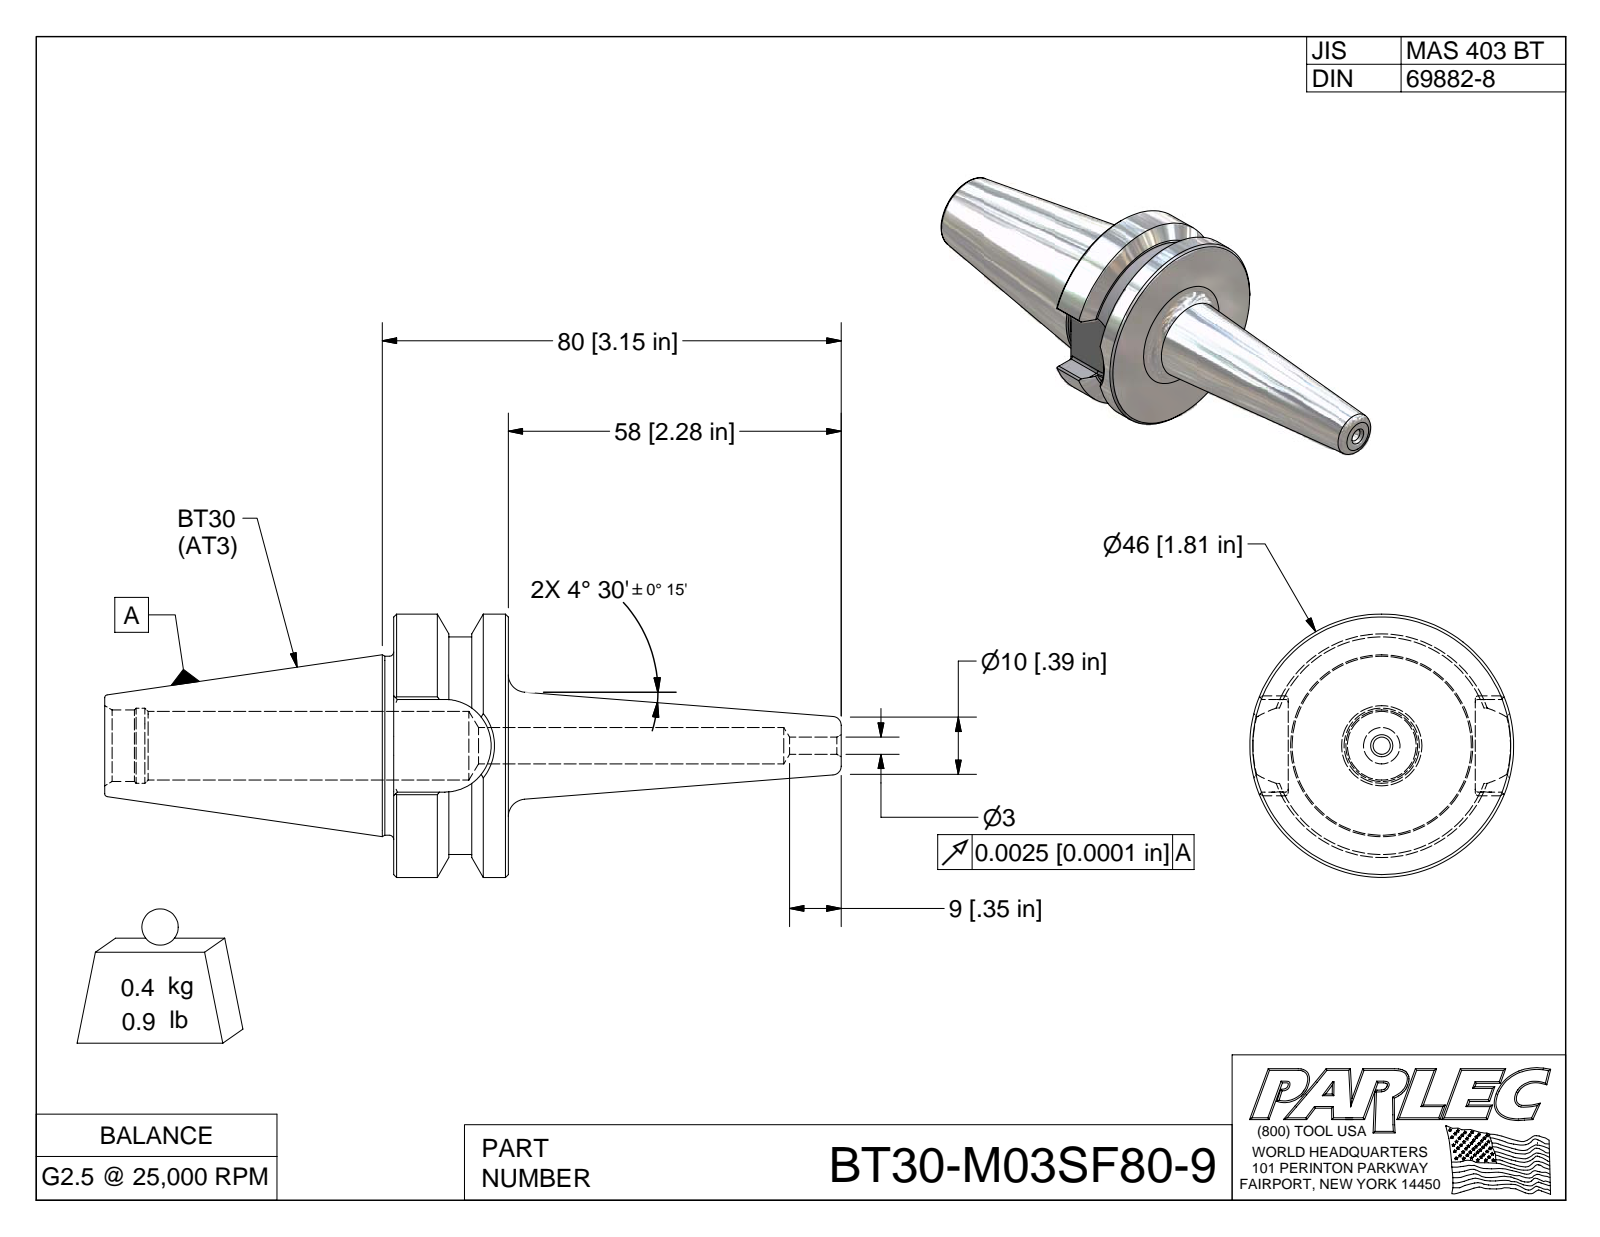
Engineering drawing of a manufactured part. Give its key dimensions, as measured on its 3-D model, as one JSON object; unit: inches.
{"part_name": "BT30-M03SF80-9; BT30-M03SF80-9-1", "step_written_by": "Autodesk Inventor 2009 (AUTOMOTIVE_DESIGN)", "units": "inches", "bodies": {"solids": 1, "faces": 68, "planar": 23, "cylindrical": 18, "other": 27}, "overall_size": [5.056, 1.811, 1.811], "volume_in3": 3.293, "surface_area_in2": 24.77, "round_holes": [[0.118, 1], [0.517, 1]], "round_bosses_or_shafts": [[1.811, 1], [1.23, 1]], "partial_cylinders_radius": [[0.02, 8], [0.319, 1], [0.748, 1]], "face_to_face_distances": [0.787, 1.283, 1.984, 2.771, 0.637, 2.52, 0.536, 0.251, 2.363, 0.379]}
